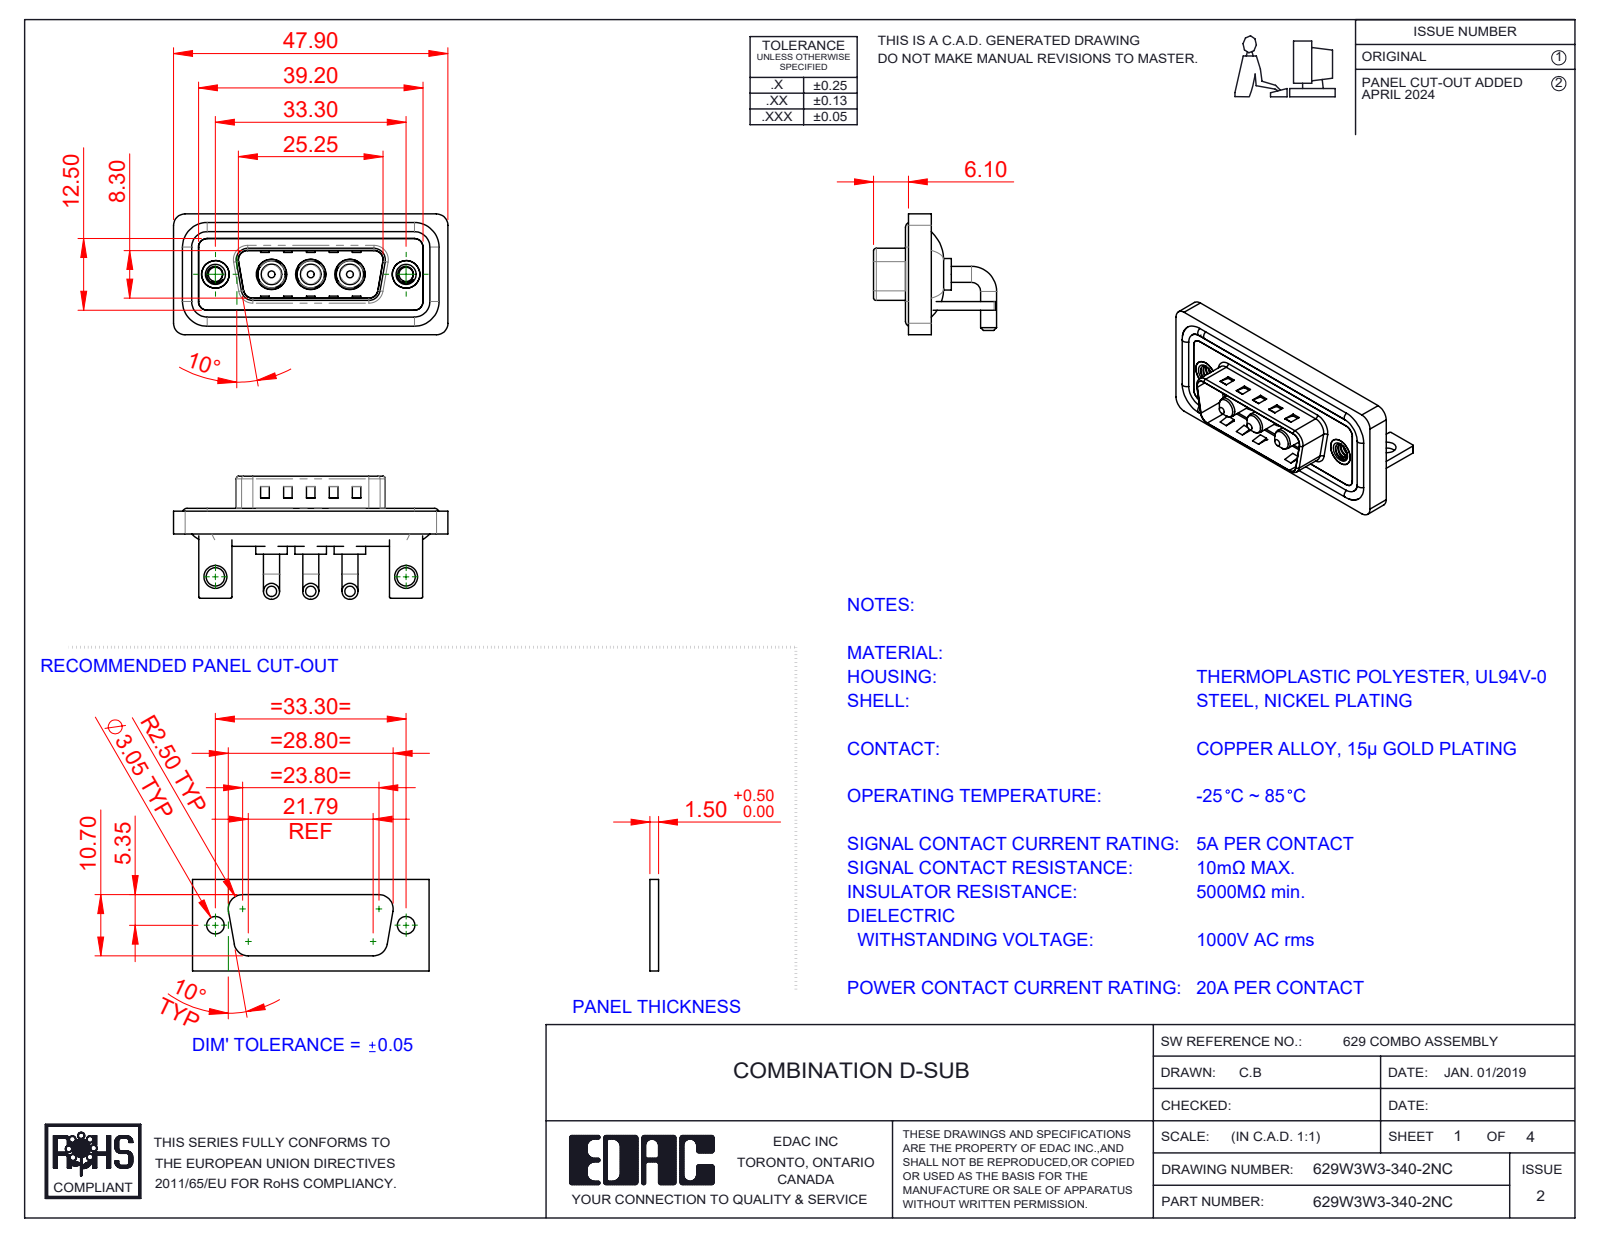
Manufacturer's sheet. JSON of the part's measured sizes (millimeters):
{"part_name": "629Combo Housing_3W3; 629W3W3-340-2NC; Power Pin_20A RA; 629Combo Waterproof Housing_15 Contacts (+4 more)", "step_written_by": "SolidWorks 2023 (CONFIG_CONTROL_DESIGN)", "units": "millimeters", "bodies": {"solids": 15, "faces": 614, "planar": 227, "cylindrical": 265, "other": 122}, "overall_size": [47.9, 21.5, 21.1], "volume_mm3": 6050, "surface_area_mm2": 9624, "round_holes": [[4.85, 3], [5.3, 3], [2.5, 2], [3.2, 2], [4, 2], [4.8, 2], [5, 2]], "round_bosses_or_shafts": [[2.8, 6], [1.6, 4], [5.5, 3], [5.2, 3], [4.75, 3], [3.75, 3], [3.6, 3], [4.9, 2]], "partial_cylinders_radius": [[2, 21], [1.5, 18], [0.25, 16], [0.5, 9], [1.6, 8], [0.6, 4], [0.65, 4], [0.9, 4]], "face_to_face_distances": [0.4, 1.5, 0.8, 2.9, 1.1, 2.1, 3.7, 1.6, 1.2, 4.5], "hole_center_spacings": [6.85, 9.8, 16.65, 23.5, 33.3, 13.7]}
